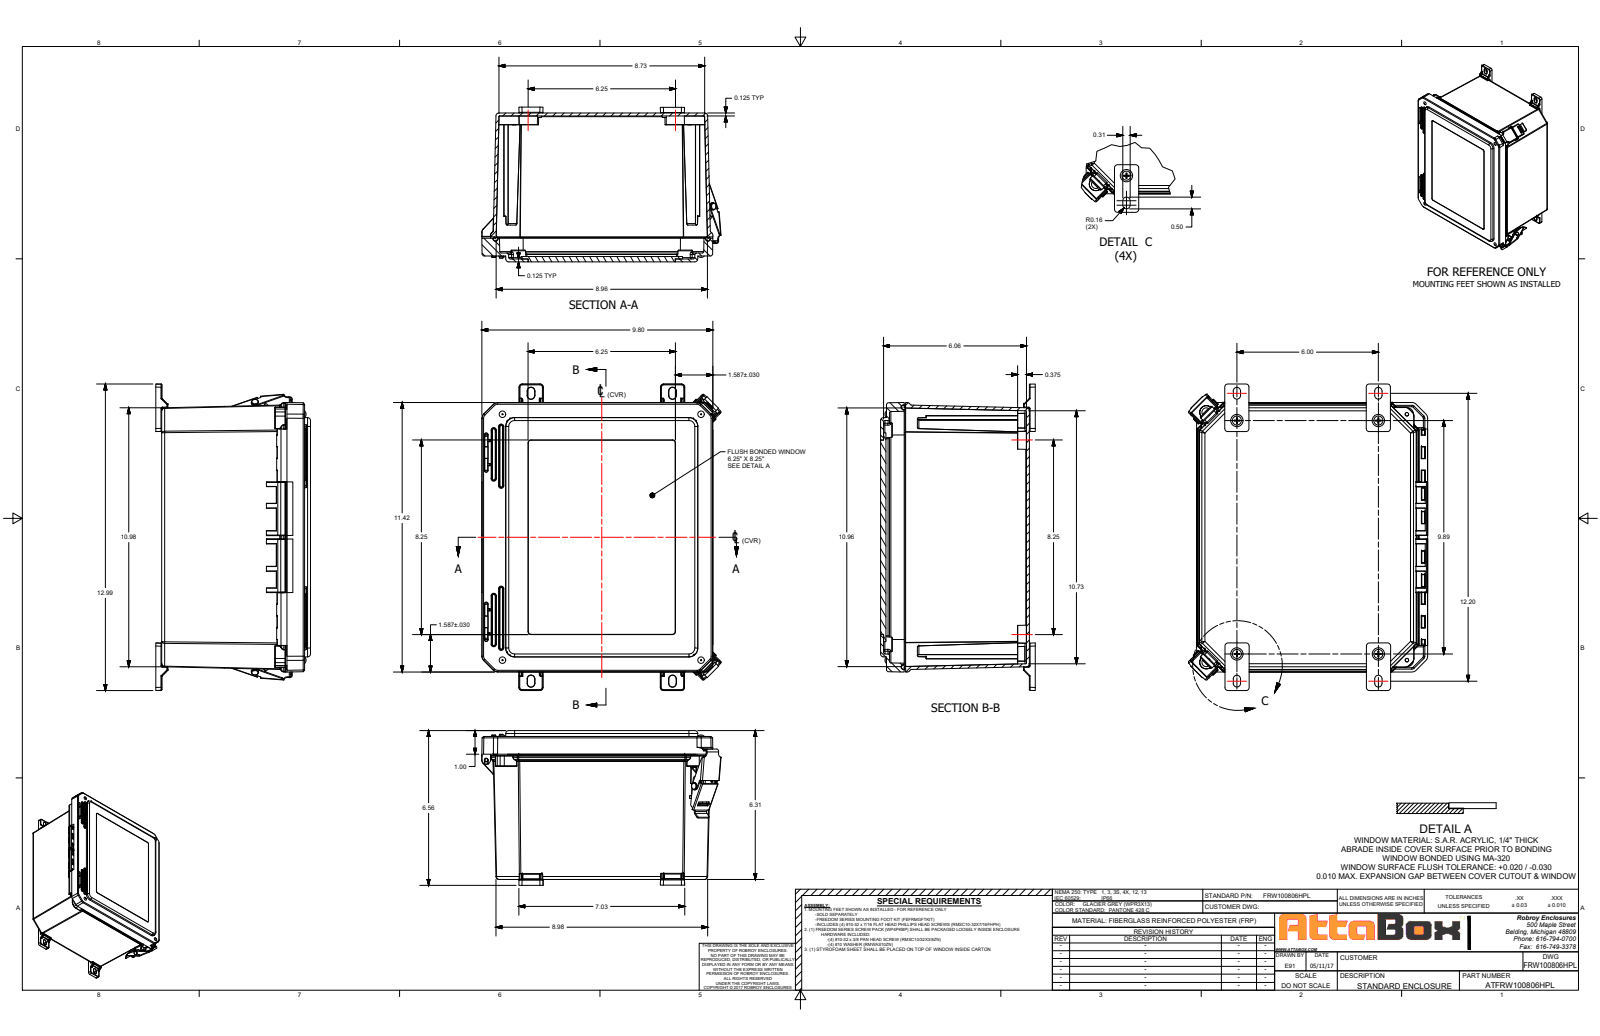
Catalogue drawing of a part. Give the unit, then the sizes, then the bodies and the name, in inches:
Units: inches
Overall size (bounding box): 12.112 × 10.142 × 6.597
Round holes (diameter × count): ⌀0.135 ×8, ⌀0.152 ×8, ⌀0.159 ×8, ⌀0.135 ×4, ⌀0.15 ×4, ⌀0.156 ×4, ⌀0.252 ×4, ⌀0.253 ×4, ⌀0.137 ×3, ⌀0.219 ×2, ⌀0.227 ×2, ⌀0.313 ×2
Round bosses / shafts (diameter × count): ⌀0.27 ×8, ⌀0.87 ×4, ⌀0.3 ×4, ⌀0.262 ×4, ⌀0.209 ×4, ⌀0.135 ×4, ⌀0.435 ×1, ⌀0.435 ×1
Partial cylindrical surfaces — rounded edges, fillets, slot ends (radius × count): R0.01 ×174, R0.005 ×94, R0.02 ×70, R0.03 ×69, R0.06 ×36, R0.09 ×26, R0.125 ×26, R0.03 ×24
Main face-to-face distances: 0.125, 6.183, 0.127, 6.308, 0.225, 5.959, 6.083, 6.059, 0.125, 0.126
Hole centre spacings: 9.399, 10.423, 10.229, 9.776, 10.422, 7.215, 7.415, 11.872
Volume: 76.87 in³ · Surface area: 1 036 in²
Bodies: 30 solids, 2406 faces (762 planar, 1041 cylindrical, 603 other)
Part name (STEP PRODUCT): FRW100806HPL
STEP written by: SolidWorks 2021 (AUTOMOTIVE_DESIGN)
